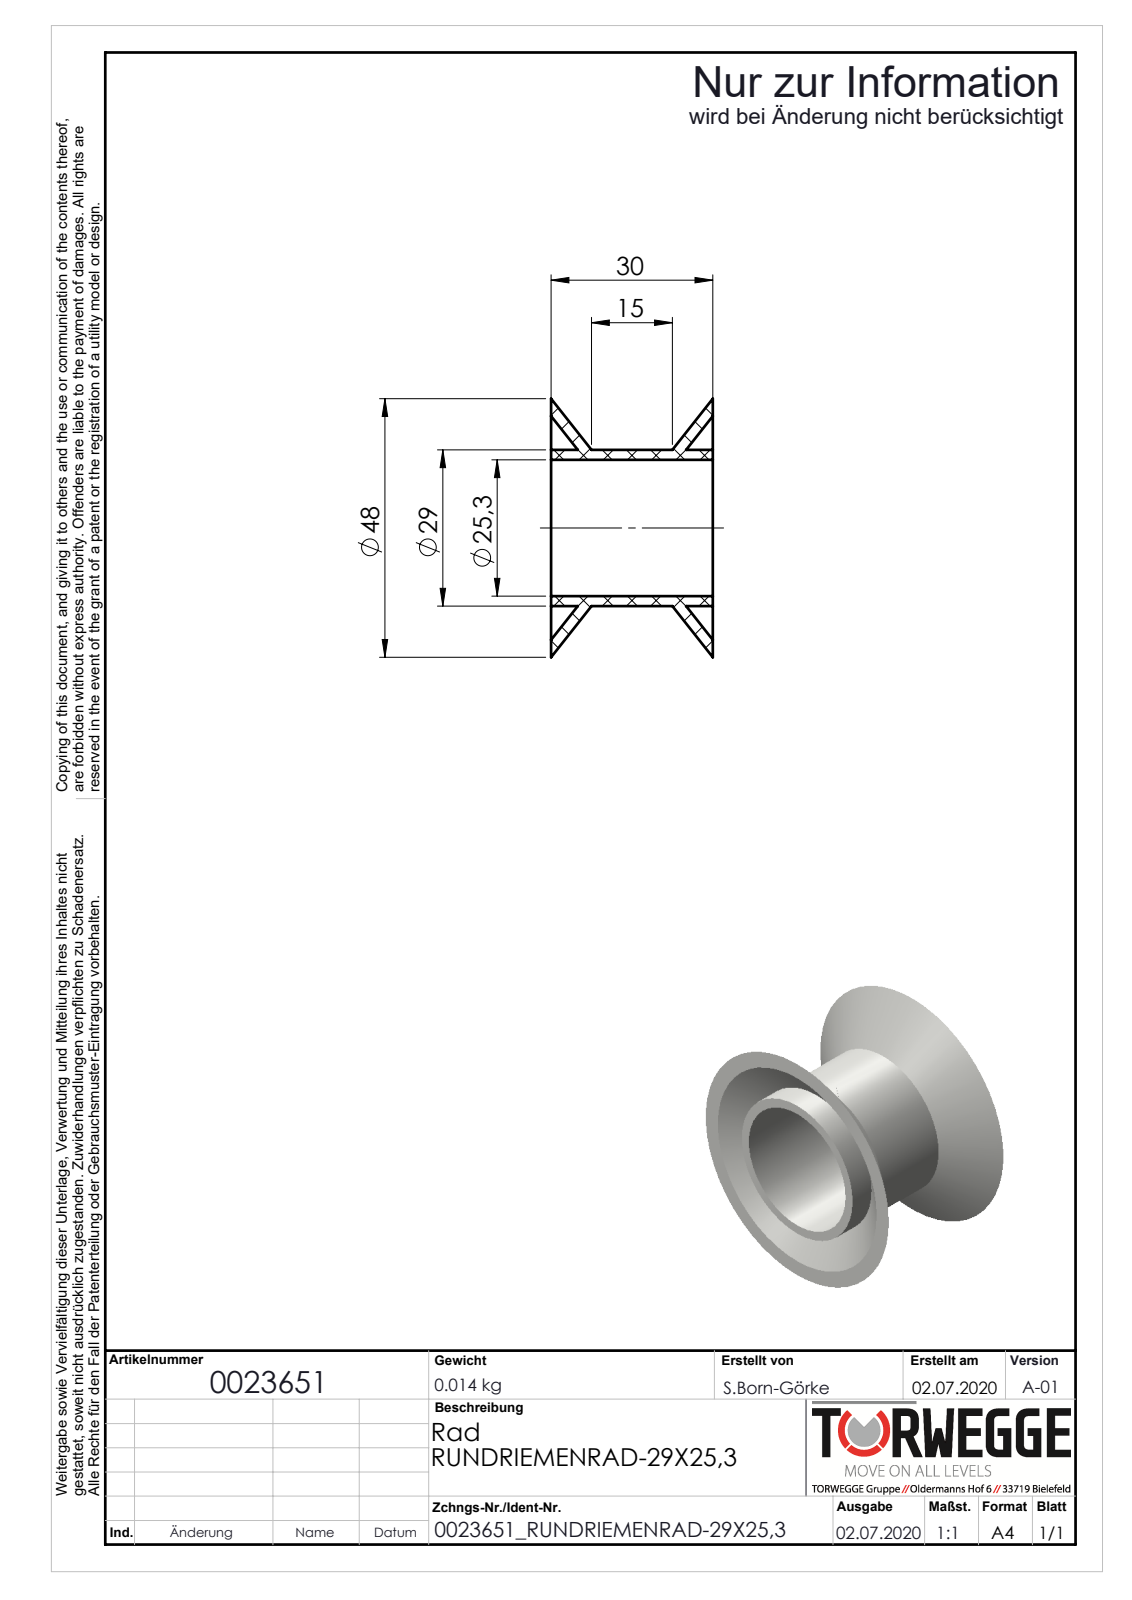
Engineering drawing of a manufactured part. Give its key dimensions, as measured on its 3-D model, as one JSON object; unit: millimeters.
{"part_name": "0023651", "step_written_by": "SolidWorks 2018 (AUTOMOTIVE_DESIGN)", "units": "millimeters", "bodies": {"solids": 1, "faces": 20, "planar": 4, "cylindrical": 8, "other": 8}, "overall_size": [48, 48, 30], "volume_mm3": 9405, "surface_area_mm2": 10576, "round_holes": [[25.3, 1]], "round_bosses_or_shafts": [[29, 1]], "face_to_face_distances": [30]}
